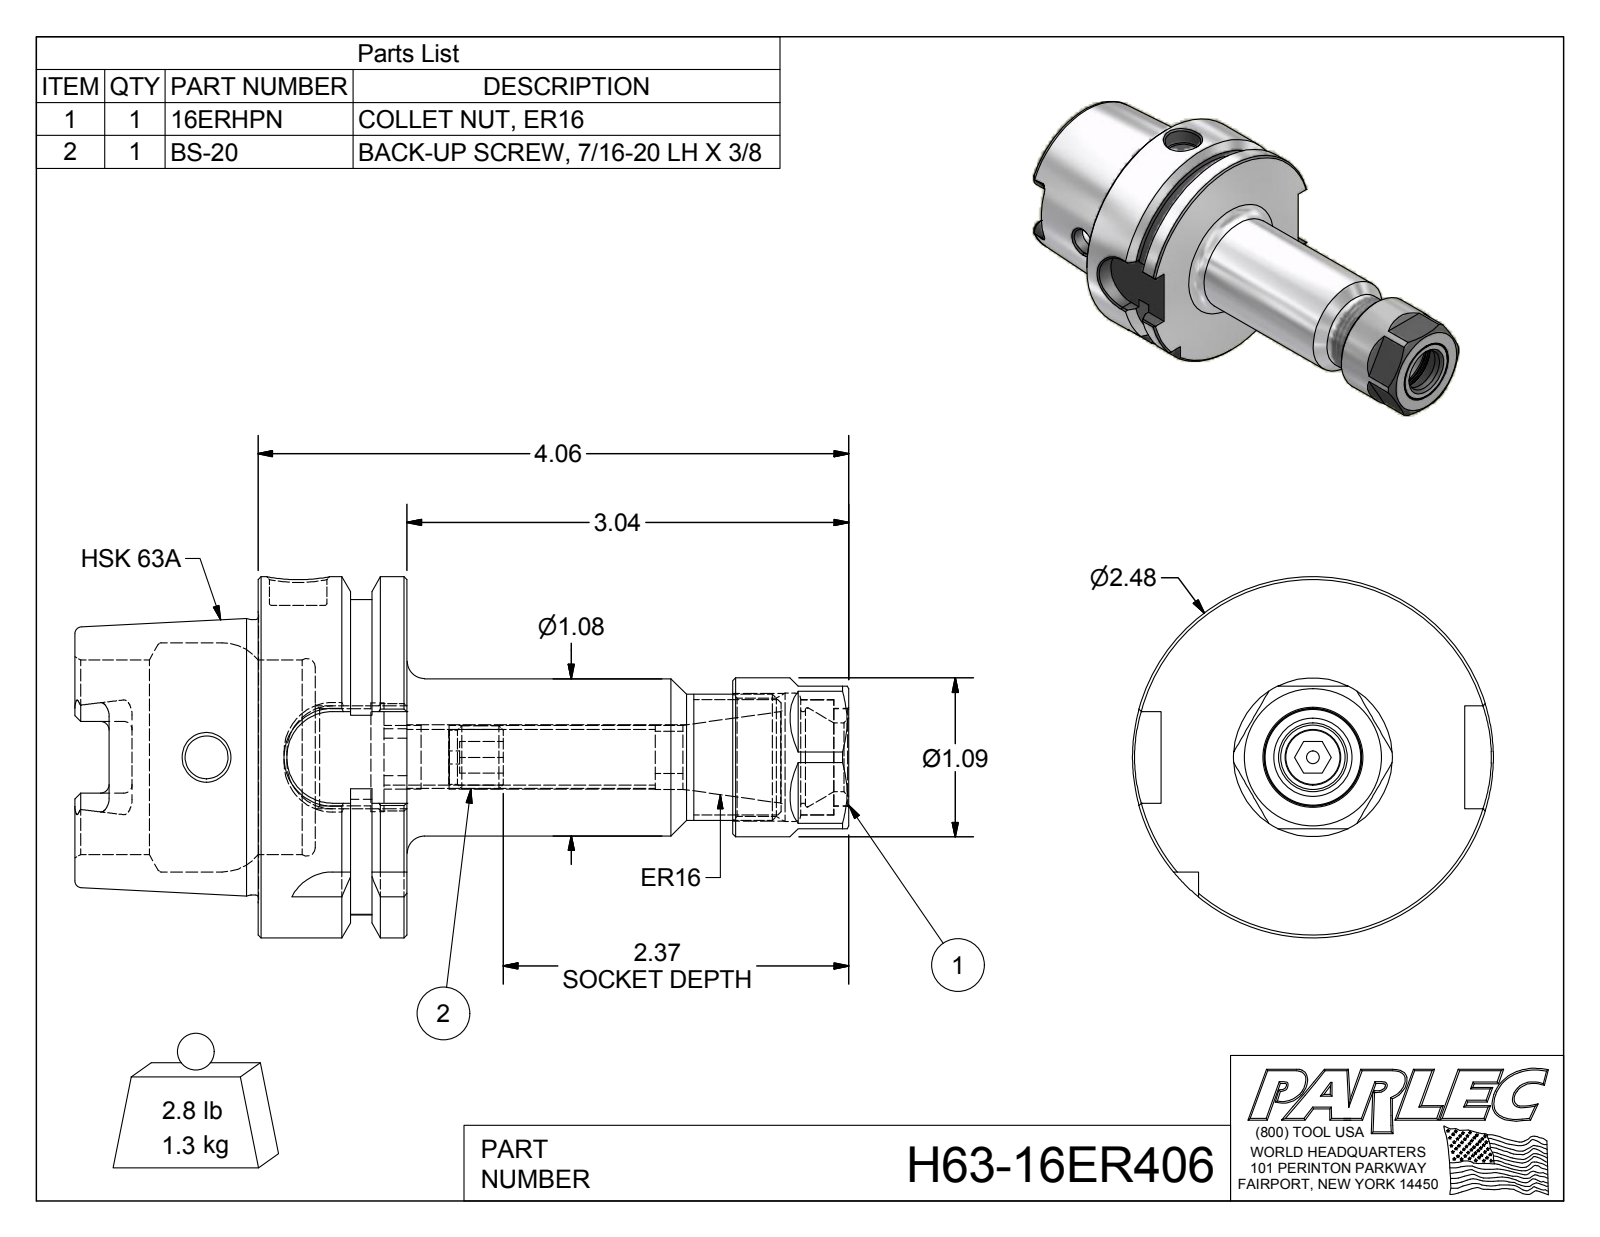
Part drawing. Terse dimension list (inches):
name: H63-16ER406; H63-16ER4-1; BS-20; 16ERHPN
written by: Autodesk Inventor 2012 (AUTOMOTIVE_DESIGN)
unit: in
bodies: 4 solids, 196 faces (86 planar, 49 cylindrical, 61 other)
size: 5.32 × 2.48 × 2.48
volume: 7.096 in³; area: 54.53 in²
holes: 1× ⌀0.09, 1× ⌀0.295, 1× ⌀0.383, 1× ⌀0.394, 1× ⌀0.44, 1× ⌀0.474, 1× ⌀0.63, 1× ⌀0.666, 1× ⌀0.674, 1× ⌀0.68, 1× ⌀0.749, 1× ⌀0.794
bosses: 1× ⌀2.48, 1× ⌀1.891, 1× ⌀1.092, 1× ⌀1.08, 1× ⌀0.866, 1× ⌀0.79, 1× ⌀0.67, 1× ⌀0.432
rounds: 6× R0.059, 4× R0.113, 4× R0.315, 1× R0.191, 1× R1.083
face distances: 1.024, 0.241, 0.389, 0.394, 0.63, 1.26, 1.654, 2.283, 2.043, 0.783
